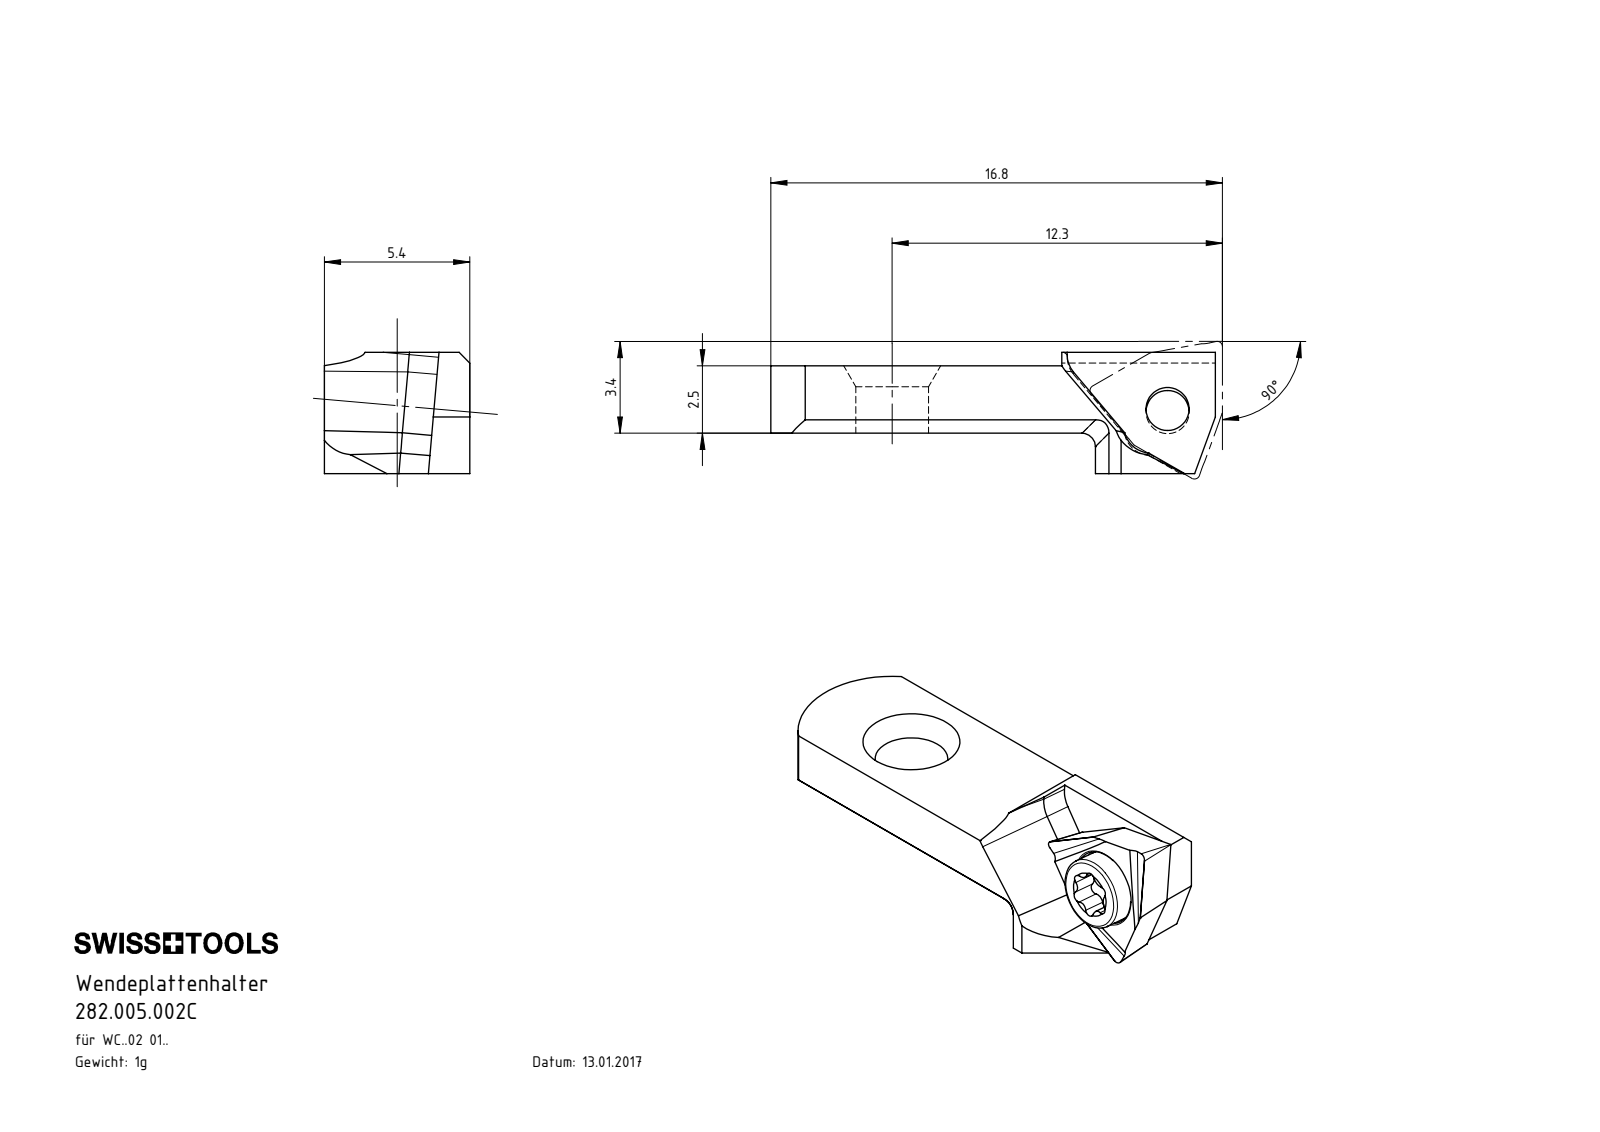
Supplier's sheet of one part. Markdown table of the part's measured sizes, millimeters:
| quantity | value |
| --- | --- |
| part name | 282.005.002C; WWA-ER2.001.004_A; F14-WWA.001.004_C; WWA-SFH.020.004 |
| STEP written by | SolidWorks 2017 (CONFIG_CONTROL_DESIGN) |
| units | millimeters |
| bodies | 3 solids, 100 faces (40 planar, 34 cylindrical, 26 other) |
| overall size | 16.76 × 5.59 × 5.11 |
| volume | 200 mm³ |
| surface area | 387 mm² |
| round holes (diameter × count) | 1.6 × 1, 2.3 × 1, 2.7 × 1 |
| round bosses / shafts (diameter × count) | 2.7 × 1, 2 × 1 |
| partial cylindrical surfaces (radius × count) | 0.17 × 6, 0.32 × 6, 0.3 × 3, 0.7 × 2, 1 × 2, 0.5 × 1, 3.5 × 1 |
| main face-to-face distances | 2.5, 5.4, 1.5, 4, 4.5, 3, 0.5, 1.59, 5.3, 2.24 |
